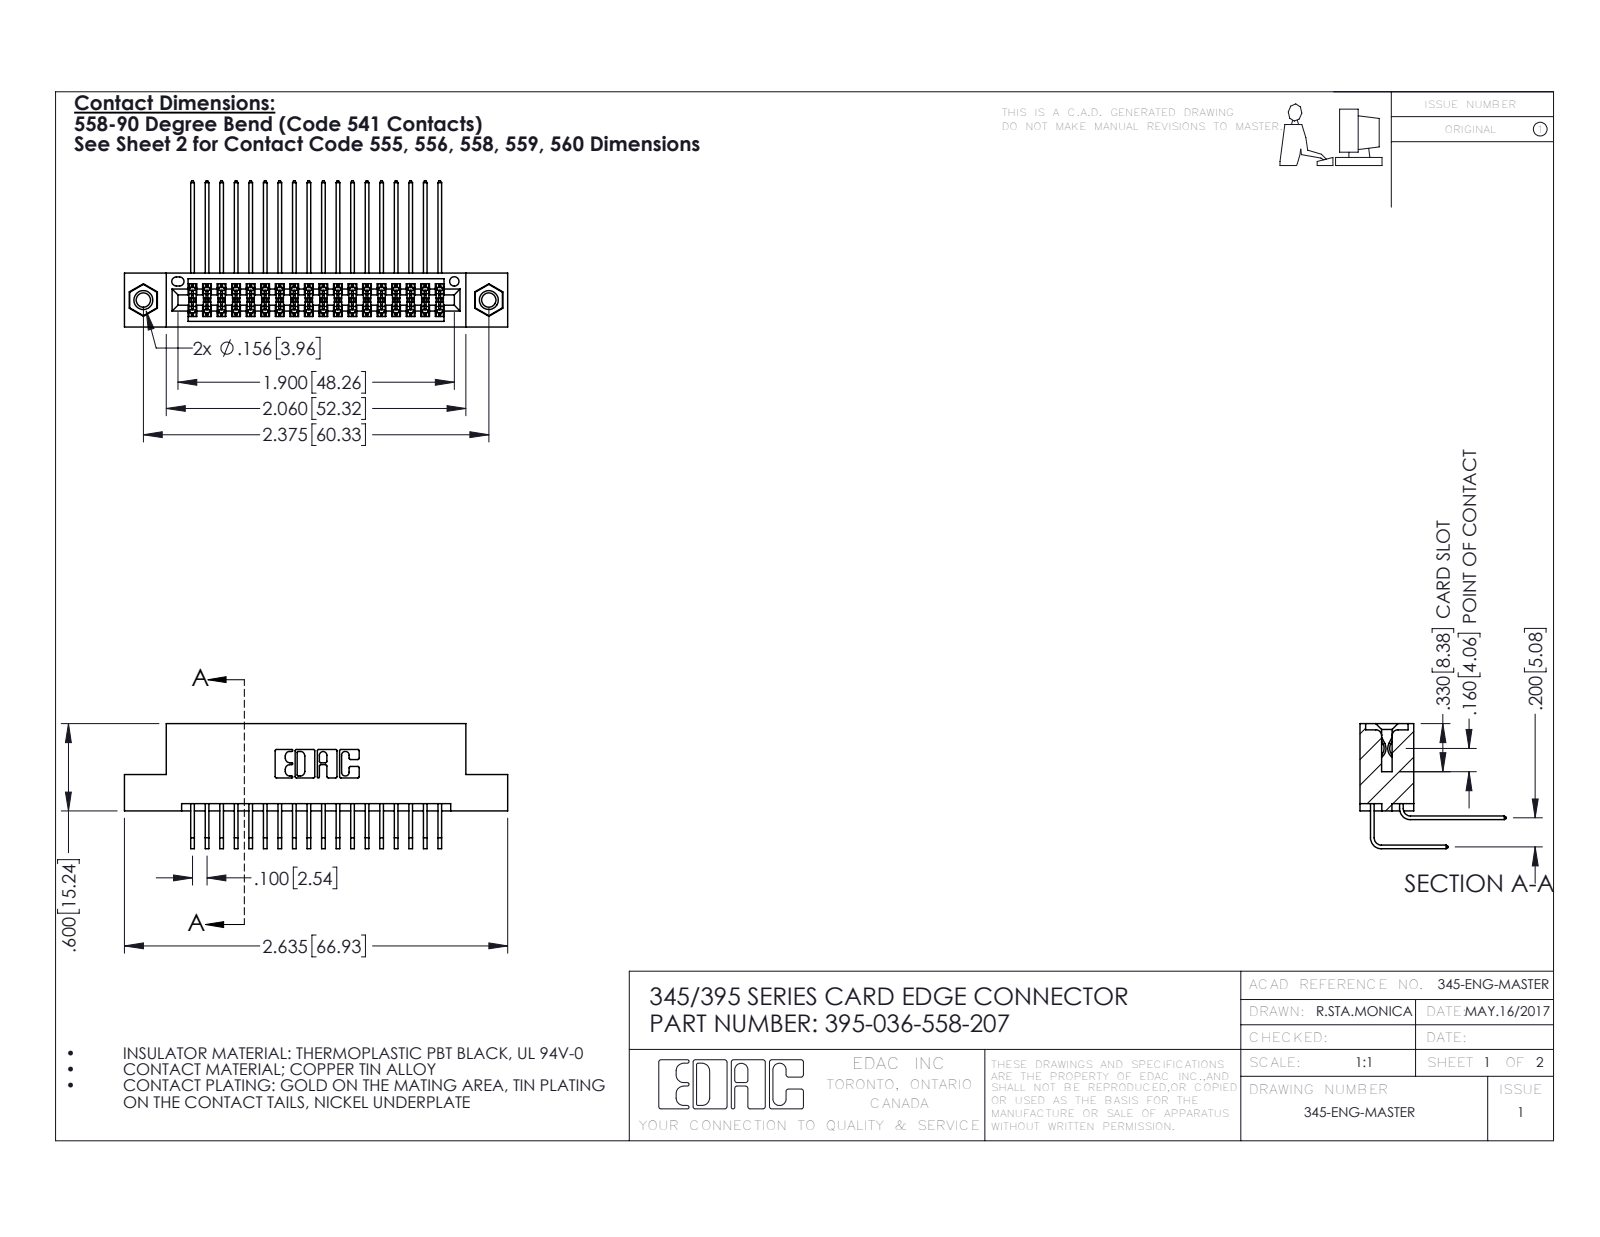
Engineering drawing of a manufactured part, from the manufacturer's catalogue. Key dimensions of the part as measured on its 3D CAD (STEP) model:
Part name (STEP PRODUCT): 345-292-001_558 559 Tail - 1; 345 Part_Flush Mounting Lugs - 0.156 Dia-TI; 345-250-001_345-250-005-103; 345-292-001_558 Tail - 2 (+1 more)
STEP written by: SolidWorks 2016 (CONFIG_CONTROL_DESIGN)
Units: inches
Bodies: 39 solids, 2058 faces (1372 planar, 670 cylindrical, 16 other)
Overall size (bounding box): 2.635 × 1.005 × 0.859
Volume: 0.395 in³ · Surface area: 15.67 in²
Round holes (diameter × count): ⌀0.098 ×2, ⌀0.125 ×2, ⌀0.156 ×2, ⌀0.064 ×1
Round bosses / shafts (diameter × count): ⌀0.155 ×2
Partial cylindrical surfaces — rounded edges, fillets, slot ends (radius × count): R0.006 ×55, R0.01 ×22, R0.007 ×6, R0.031 ×6, R0.026 ×3, R0.014 ×2, R0.019 ×2, R0.022 ×2
Main face-to-face distances: 0.2, 0.072, 0.298, 0.37, 0.098, 0.272, 0.025, 0.225, 0.285, 0.1
Hole centre spacings: 0.27, 2.141, 2.375
